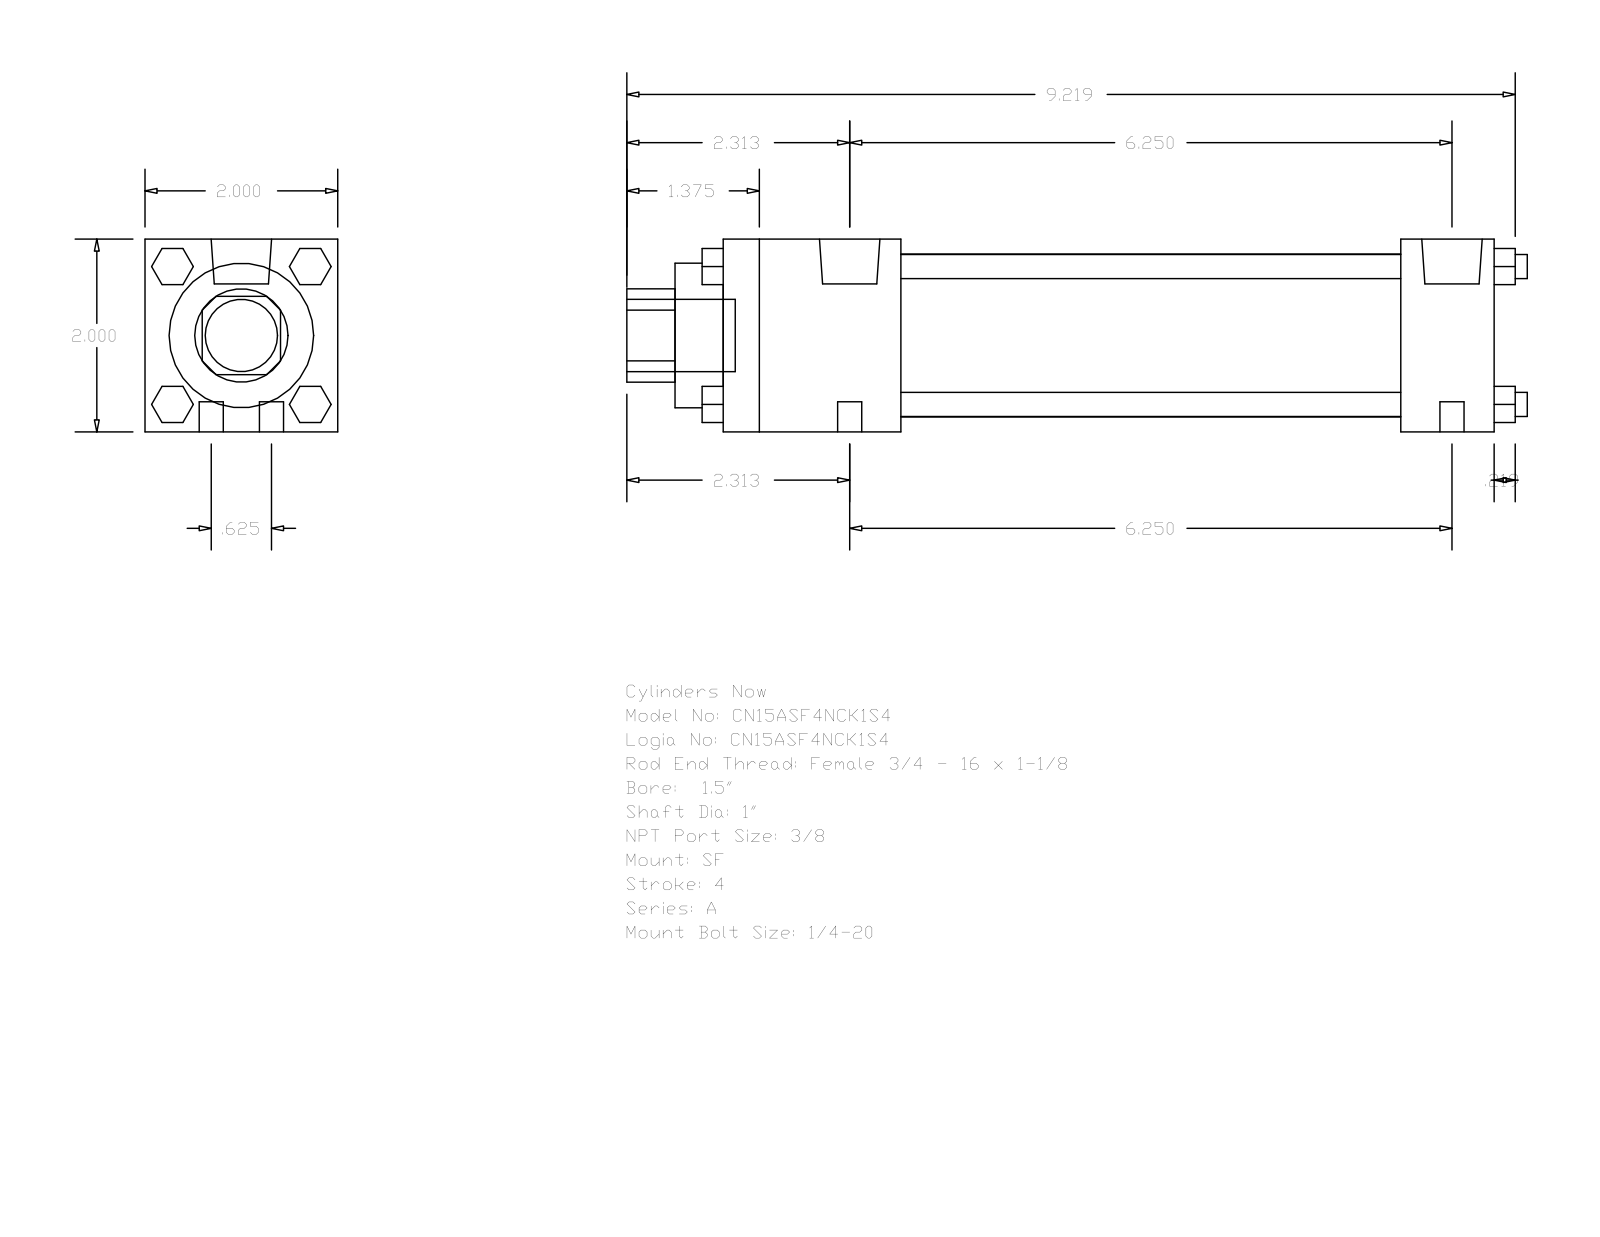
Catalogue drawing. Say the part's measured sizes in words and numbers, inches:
The part is named "A_SF__0150_1". Its 3-D file was written by "GSSL Pune (CONFIG_CONTROL_DESIGN)". It is 0 solids with 124 faces: 94 planar, 30 cylindrical and 0 other. Overall it measures 9.344 by 2 by 2 inches. Round holes: 1 of diameter 1, 1 of diameter 1.5, 1 of diameter 1.69. Round bosses or shafts: 8 of diameter 0.25, 2 of diameter 0.627, 2 of diameter 0.219, 1 of diameter 0.75. Partial cylindrical surfaces (rounded edges, fillets, slot ends): 1 of radius 0.484. The main face-to-face distances are 2, 8, 1.844, 7.031, 5.187, 6.156, 0.969, 0.5, 2.344, 7.531.
